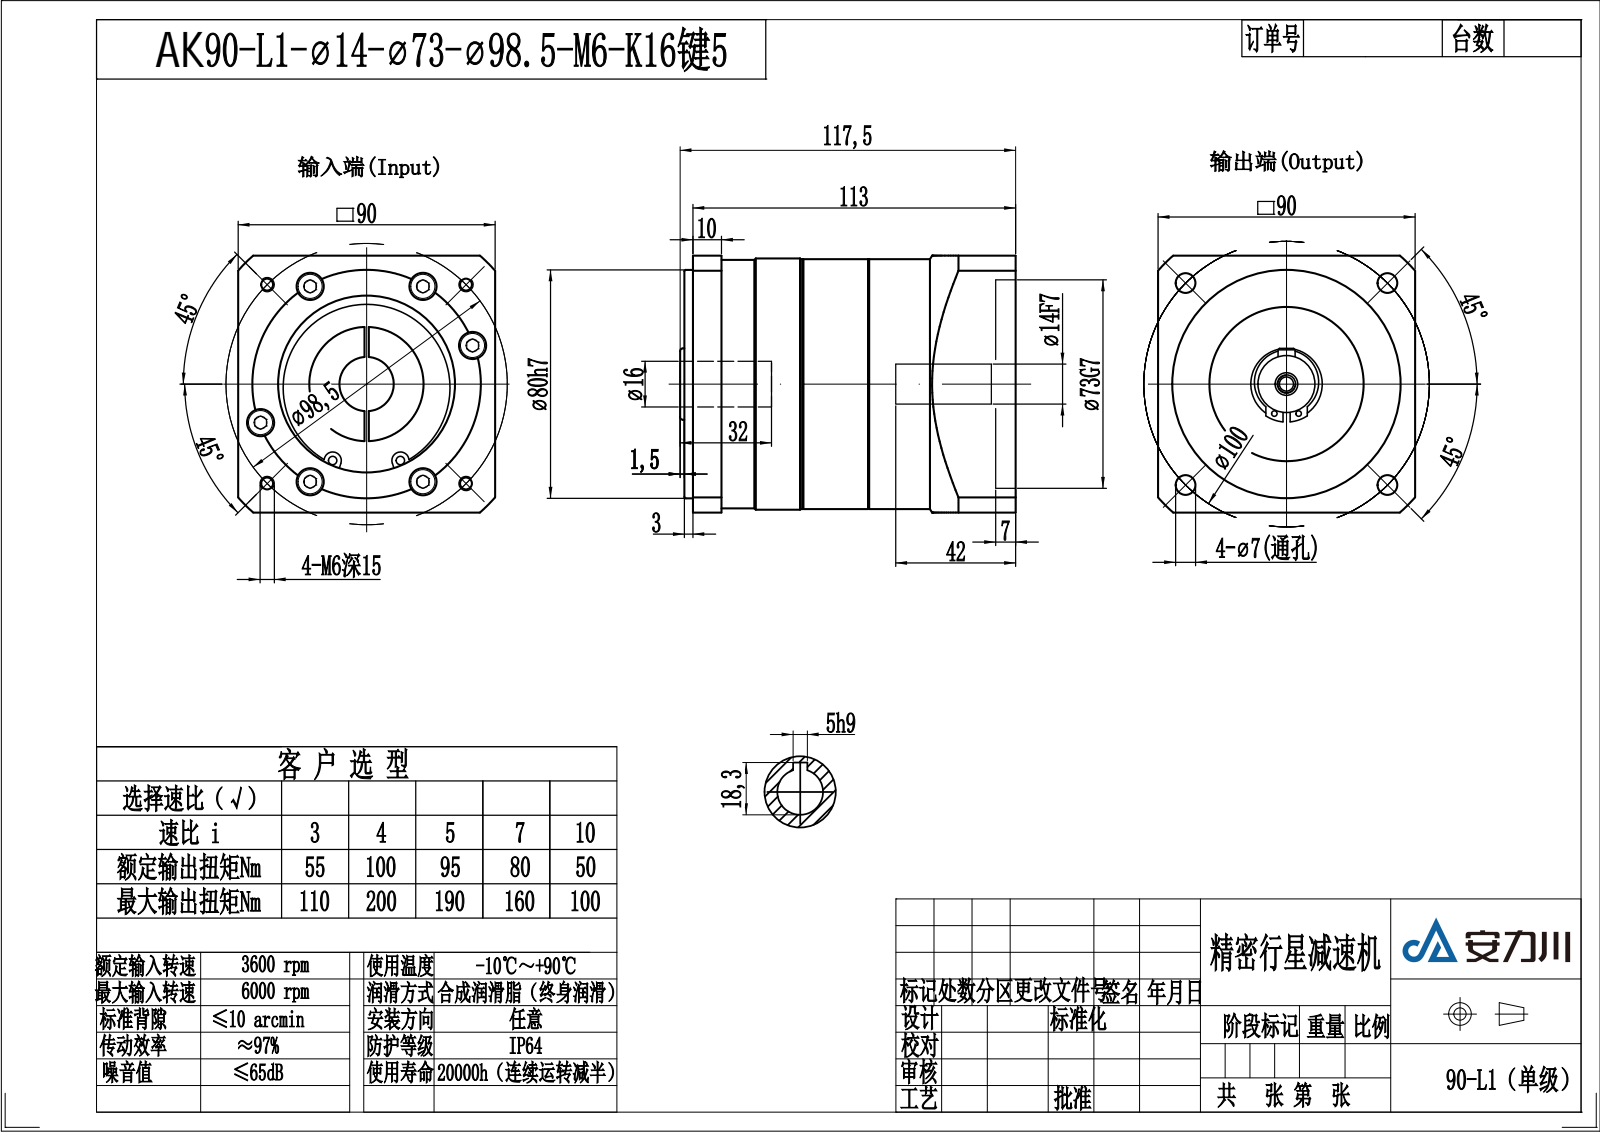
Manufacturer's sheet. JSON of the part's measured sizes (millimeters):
{"part_name": "circlips for shaft--type a large gb_GB_CONNECTING_PIECE_RING_RRA 25_2; 6007_2; 090齿圈-L1_1; hexagon socket head cap screws gb_GB_FASTENER_SCREWS_HSHCS M5X50-N_2 (+8 more)", "step_written_by": "SolidWorks 2014 (AUTOMOTIVE_DESIGN)", "units": "millimeters", "bodies": {"solids": 23, "faces": 987, "planar": 270, "cylindrical": 331, "other": 386}, "overall_size": [117.5, 90, 90], "volume_mm3": 533547, "surface_area_mm2": 167300, "round_holes": [[4.2, 8], [5.5, 8], [5.4, 6], [9.5, 6], [6, 5], [5, 4], [7, 4], [2, 2], [12, 2], [2.5, 1], [14, 1], [16, 1]], "round_bosses_or_shafts": [[8.5, 8], [5, 8], [8, 6], [88, 1], [87.5, 1], [87, 1], [80, 1], [44, 1]], "partial_cylinders_radius": [[2.5, 4], [0.5, 2], [1, 2], [4.5, 2], [36.5, 1], [60, 1]], "face_to_face_distances": [90, 3, 51.5, 64.5, 20, 41.5, 61.5, 32, 23, 44.5], "hole_center_spacings": [39.5, 70.18, 0.75, 69.65, 70.71, 99.25, 25.45, 44.08]}
